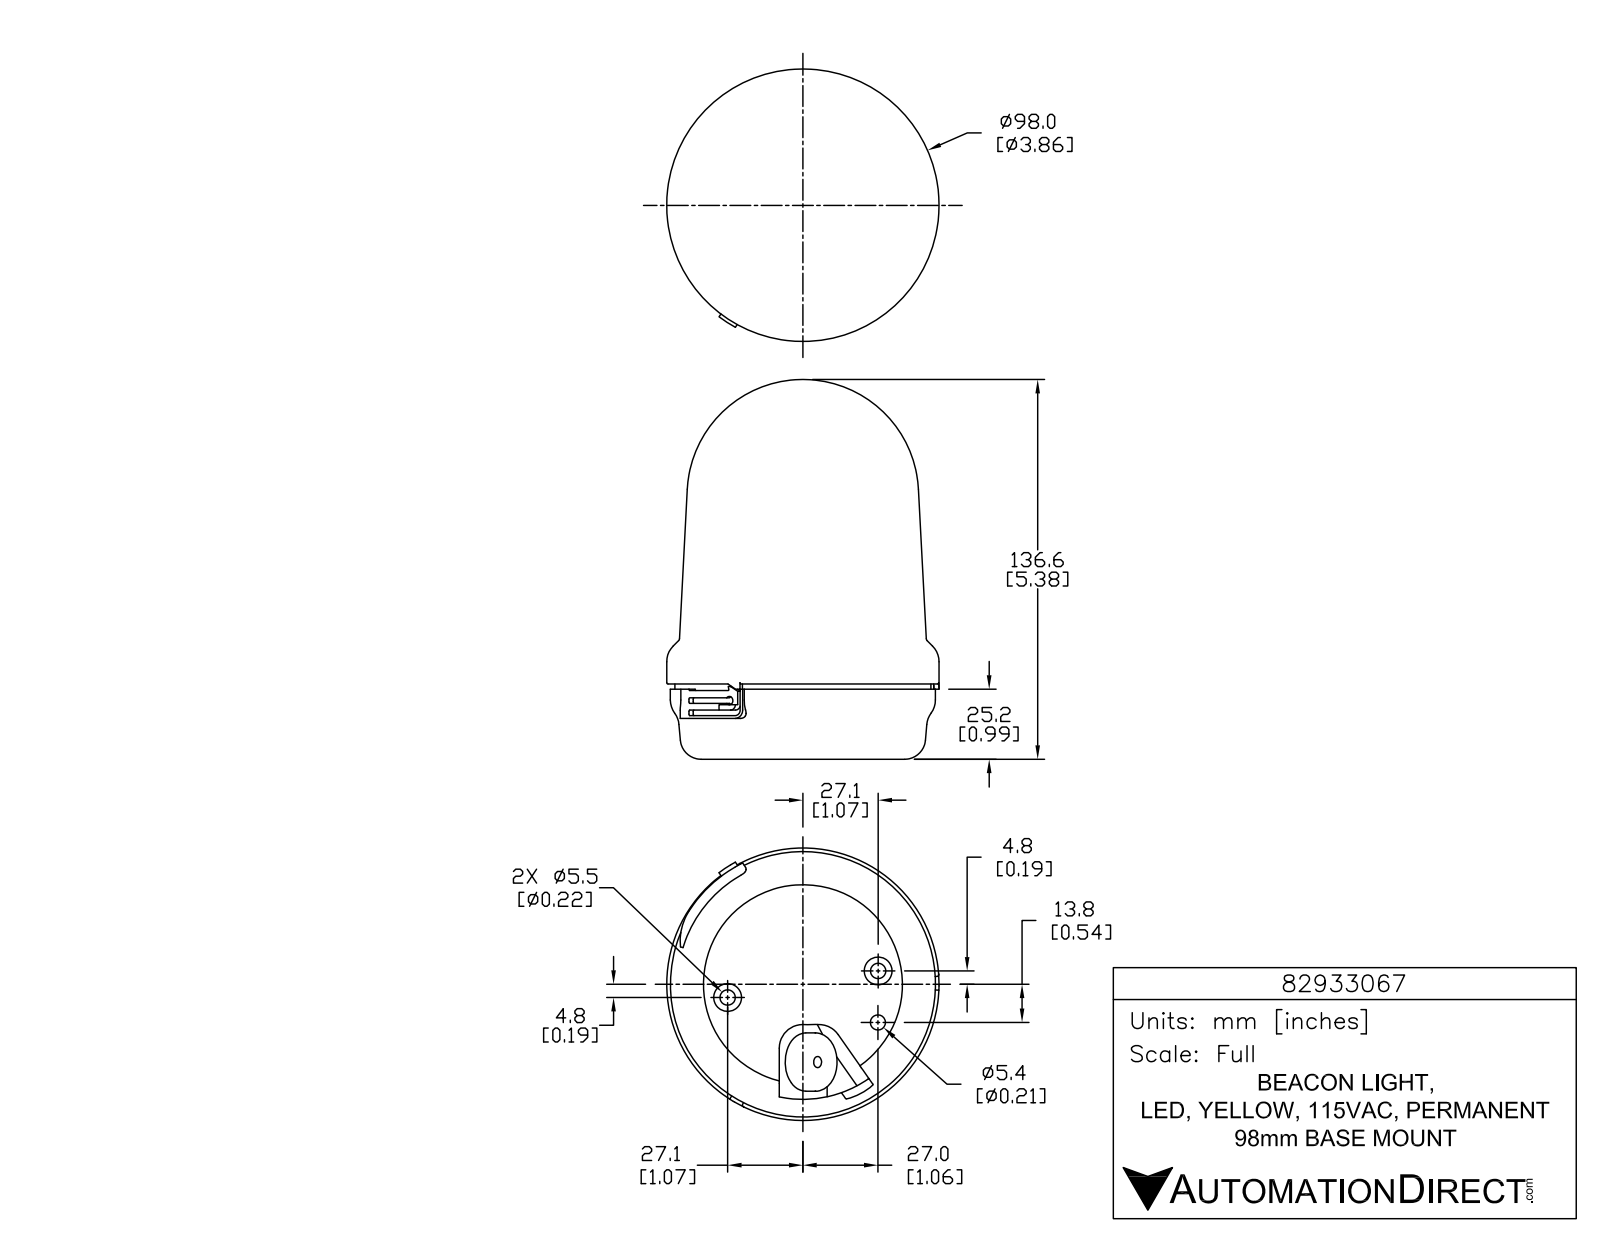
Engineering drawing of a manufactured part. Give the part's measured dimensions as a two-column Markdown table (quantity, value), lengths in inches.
| quantity | value |
| --- | --- |
| part name | 82933067 |
| STEP written by | SolidWorks 2015 (AUTOMOTIVE_DESIGN) |
| units | inches |
| bodies | 1 solid, 872 faces (566 planar, 204 cylindrical, 102 other) |
| overall size | 5.378 × 3.858 × 3.858 |
| volume | 44.69 in³ |
| surface area | 73.66 in² |
| round holes (diameter × count) | 0.059 × 3, 0.217 × 2, 0.157 × 1, 0.213 × 1, 2.819 × 1 |
| round bosses / shafts (diameter × count) | 0.339 × 3, 0.084 × 3, 0.394 × 2, 3.858 × 1, 3.756 × 1, 3.626 × 1, 0.827 × 1 |
| partial cylindrical surfaces (radius × count) | 0.005 × 9, 0.005 × 6, 0.012 × 6, 0.012 × 6, 0.012 × 6, 0.196 × 6, 0.02 × 5, 0.039 × 4 |
| main face-to-face distances | 1.045, 0.972, 0.073, 0.02, 0.992, 1.065, 0.236, 0.579, 0.559, 0.413 |
| hole center spacings | 1.083, 0.73, 1.193, 2.158, 2.165 |
